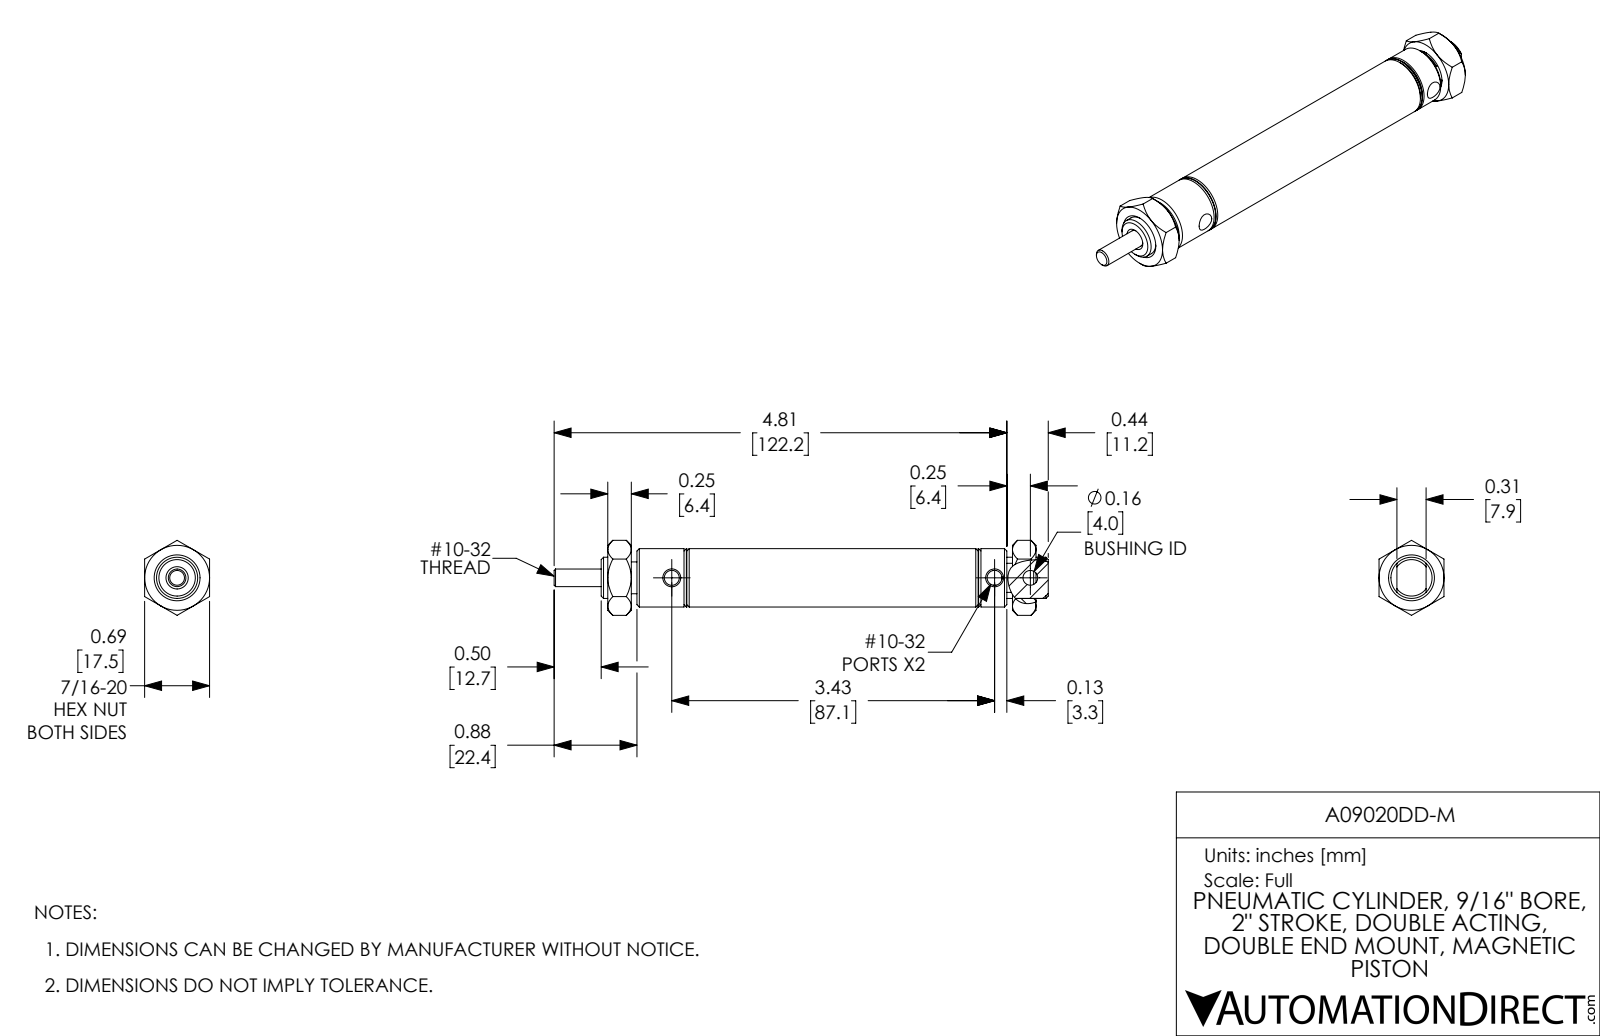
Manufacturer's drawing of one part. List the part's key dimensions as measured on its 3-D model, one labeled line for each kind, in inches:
Part name (STEP PRODUCT): A09020DD-M; A09020DD-M_Mounting Nut_D-154; A09020DD-M-Rod; A09020DD-M-MainBody
STEP written by: SolidWorks 2017 (AUTOMOTIVE_DESIGN)
Units: inches
Bodies: 4 solids, 151 faces (36 planar, 46 cylindrical, 69 other)
Overall size (bounding box): 5.25 × 0.797 × 0.69
Volume: 0.957 in³ · Surface area: 21.94 in²
Round holes (diameter × count): ⌀0.159 ×2, ⌀0.19 ×2, ⌀0.156 ×1, ⌀0.157 ×1, ⌀0.187 ×1, ⌀0.563 ×1
Round bosses / shafts (diameter × count): ⌀0.62 ×1, ⌀0.437 ×1, ⌀0.338 ×1
Main face-to-face distances: 0.69, 0.5, 0.25, 4.3, 0.715, 3.215, 3.275, 0.31, 2.5, 0.775
Hole centre spacings: 0.38, 3.43, 3.81
